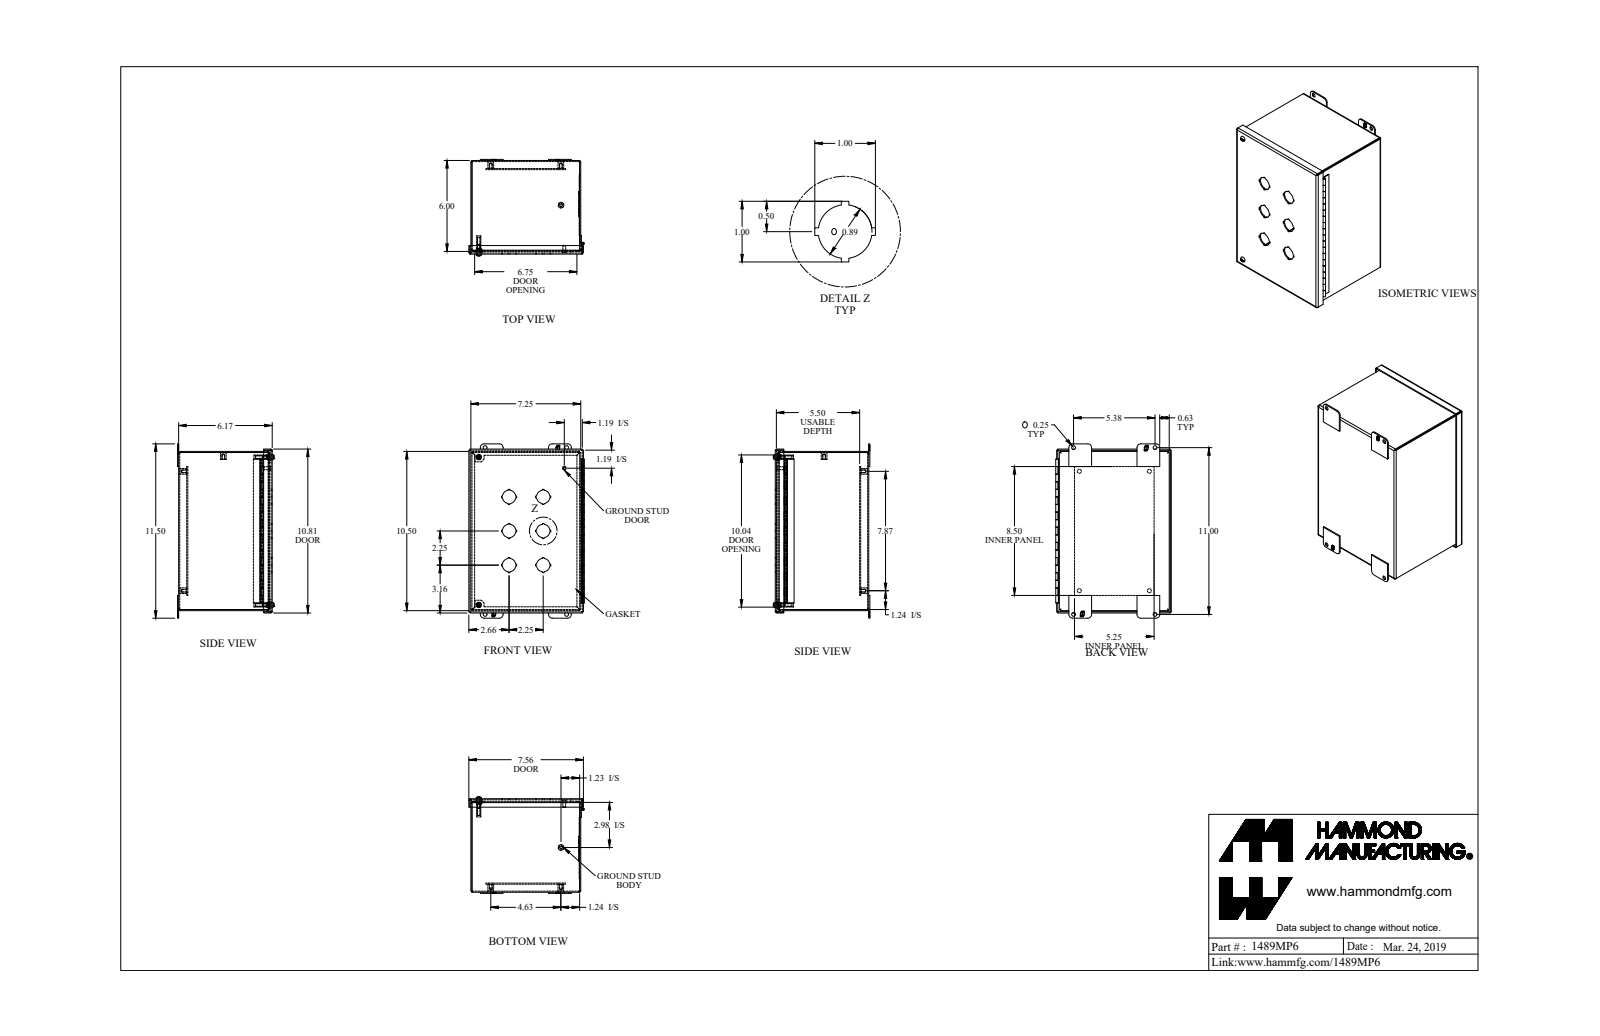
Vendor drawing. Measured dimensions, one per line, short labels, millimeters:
name: 1489MP6_Default
written by: SolidWorks 2019 (CONFIG_CONTROL_DESIGN)
unit: mm
bodies: 19 solids, 660 faces (408 planar, 194 cylindrical, 58 other)
size: 292.1 × 193.6 × 161.8
volume: 603 900 mm³; area: 631 400 mm²
holes: 6× ⌀6.4, 6× ⌀22.5, 5× ⌀4, 4× ⌀6.7, 2× ⌀4, 2× ⌀10.3
bosses: 5× ⌀9.5, 2× ⌀9.9, 2× ⌀7, 2× ⌀4.8, 2× ⌀3.8, 1× ⌀6.4, 1× ⌀4.8, 1× ⌀4.4
rounds: 12× R0.9, 12× R2.7, 8× R6.4, 2× R4.1, 2× R4.3, 1× R3.2
face distances: 1.8, 154.9, 182.3, 141.4, 13.5, 156.8, 264.9, 153.1, 184.2, 180.5
hole spacings: 117.5, 133.1, 271.3, 57.2, 247.7, 40.8, 40.8, 52.1
